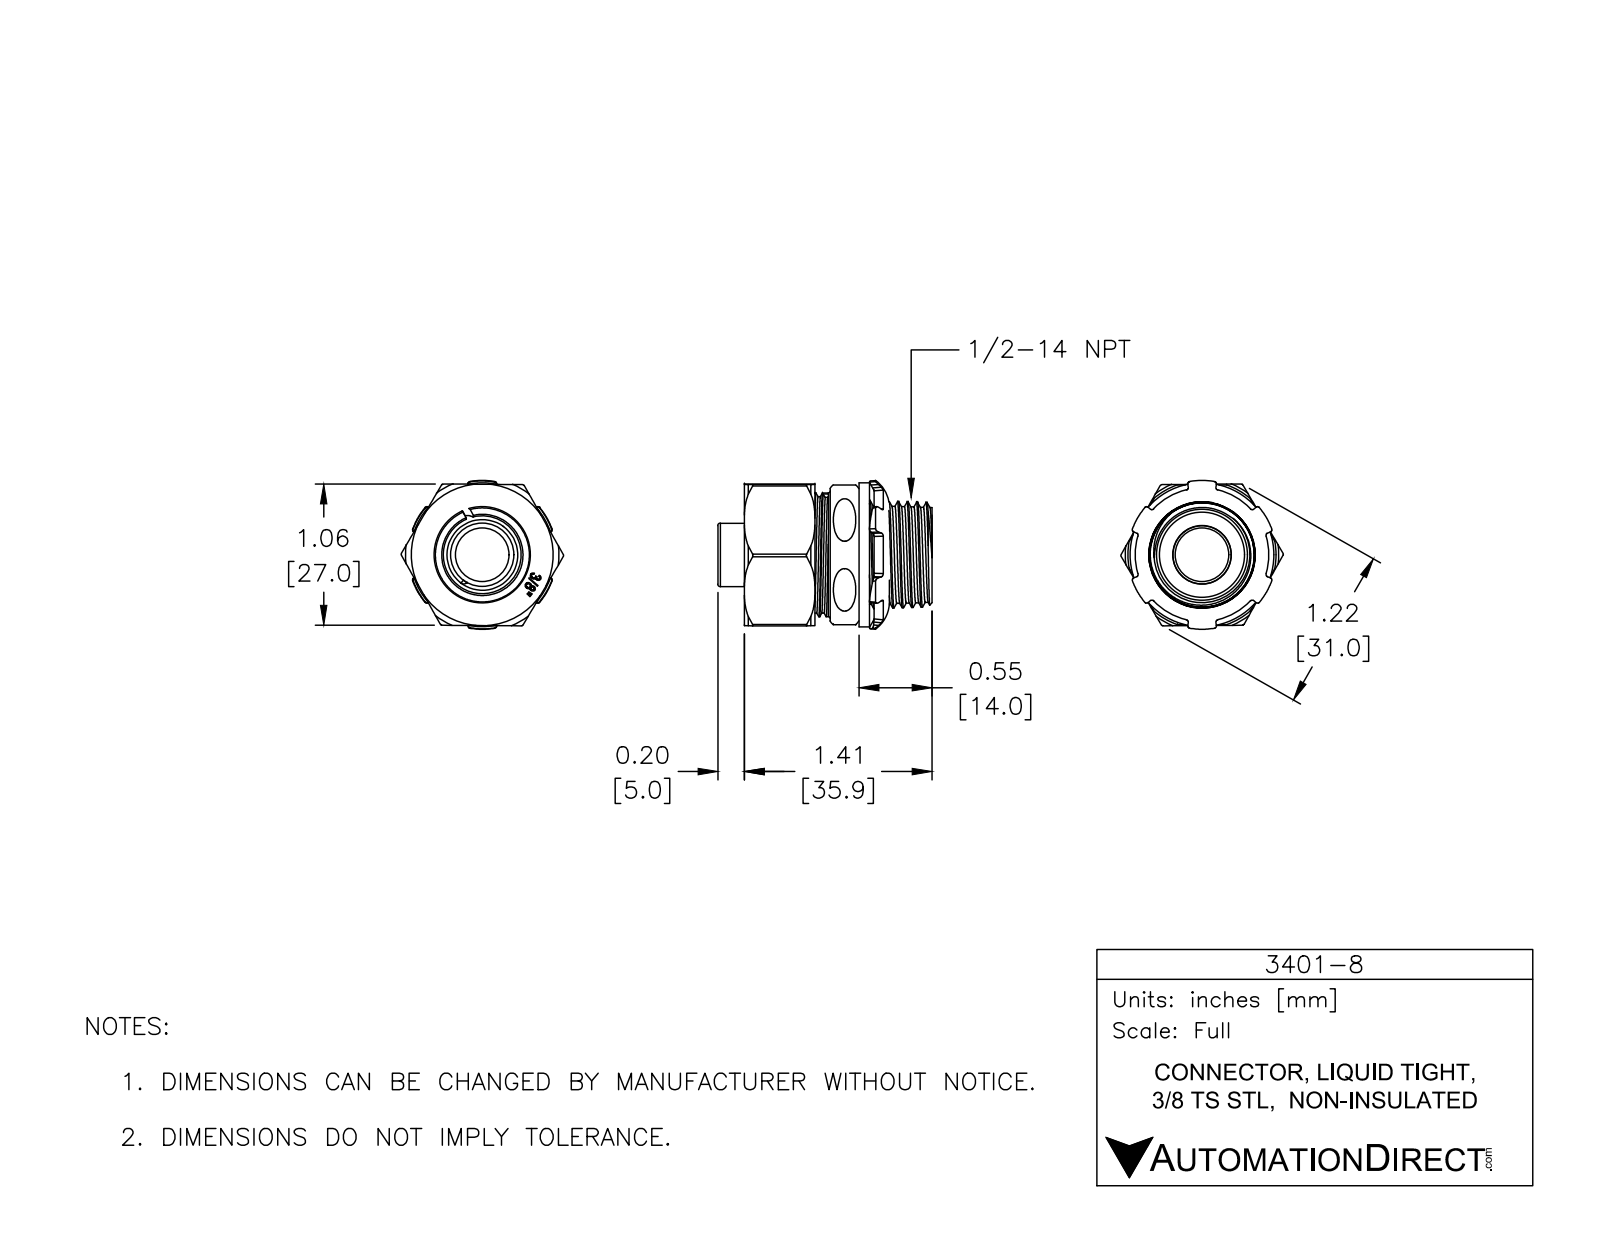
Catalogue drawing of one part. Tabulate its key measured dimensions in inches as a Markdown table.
| quantity | value |
| --- | --- |
| part name | 3401 STRAIGHT BODY; 3401-8; 3401 SEAL_3-8_1; 3401 COMPRESSION NUT HEX_3-8_1 (+3 more) |
| STEP written by | SolidWorks 2014 (AUTOMOTIVE_DESIGN) |
| units | inches |
| bodies | 6 solids, 646 faces (220 planar, 96 cylindrical, 330 other) |
| overall size | 1.611 × 1.221 × 1.119 |
| volume | 0.517 in³ |
| surface area | 21.73 in² |
| round holes (diameter × count) | 0.1 × 1, 0.402 × 1, 0.44 × 1, 0.728 × 1, 0.732 × 1, 0.787 × 1, 0.858 × 1, 0.906 × 1 |
| round bosses / shafts (diameter × count) | 1.083 × 1, 0.93 × 1, 0.866 × 1, 0.768 × 1, 0.476 × 1, 0.438 × 1, 0.081 × 1 |
| partial cylindrical surfaces (radius × count) | 0.006 × 8, 0.02 × 6, 0.034 × 2, 0.008 × 1, 0.013 × 1, 0.334 × 1 |
| main face-to-face distances | 1.063, 0.863, 0.942, 0.079, 1.063, 0.531, 0.332, 0.411, 0.071, 0.792 |
| hole center spacings | 0.453 |
